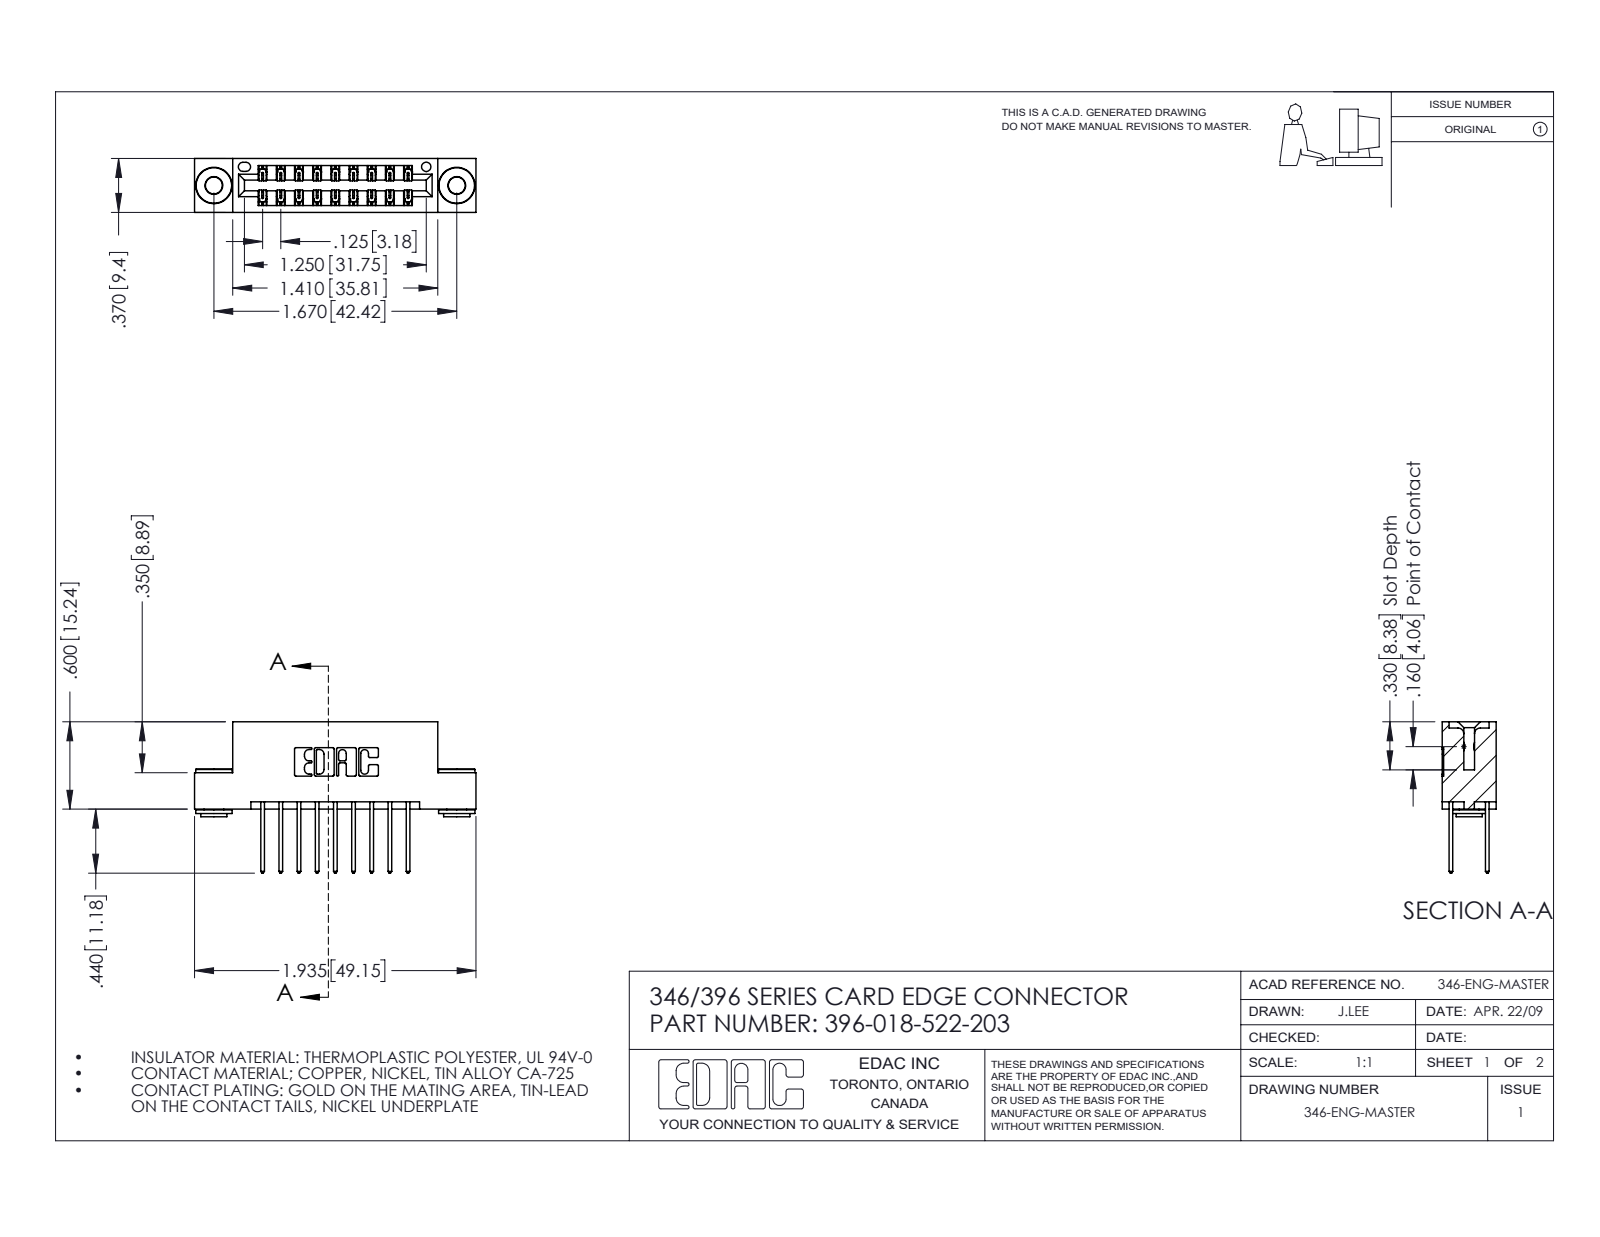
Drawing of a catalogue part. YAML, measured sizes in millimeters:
part_name: "346 Part_Flush Mounting Lugs - 0.156 Dia-TH; 396-018-522-203; 345-250-002_345-250-002-102; 345-292-001_345-293-122"
step_written_by: "SolidWorks 2016 (CONFIG_CONTROL_DESIGN)"
units: millimeters
bodies: {solids: 21, faces: 1096, planar: 716, cylindrical: 372, other: 8}
overall_size: [49.1, 26.4, 9.4]
volume: 4600
surface_area: 6235
round_holes:
  - {diameter: 2.9, count: 2}
  - {diameter: 4, count: 2}
  - {diameter: 1.6, count: 1}
round_bosses_or_shafts:
  - {diameter: 6.4, count: 2}
  - {diameter: 4.6, count: 2}
  - {diameter: 3.5, count: 2}
partial_cylinders:
  - {radius: 0.2, count: 27}
  - {radius: 0.3, count: 22}
  - {radius: 0.3, count: 18}
  - {radius: 0.2, count: 6}
  - {radius: 0.8, count: 6}
  - {radius: 0.7, count: 3}
  - {radius: 0.4, count: 2}
  - {radius: 0.6, count: 2}
face_to_face_distances: [6.4, 1.2, 8.2, 9.4, 0.6, 1.8, 7.6, 7, 3.8, 5.6]
hole_center_spacings: [6.2, 37.2, 42.4]
